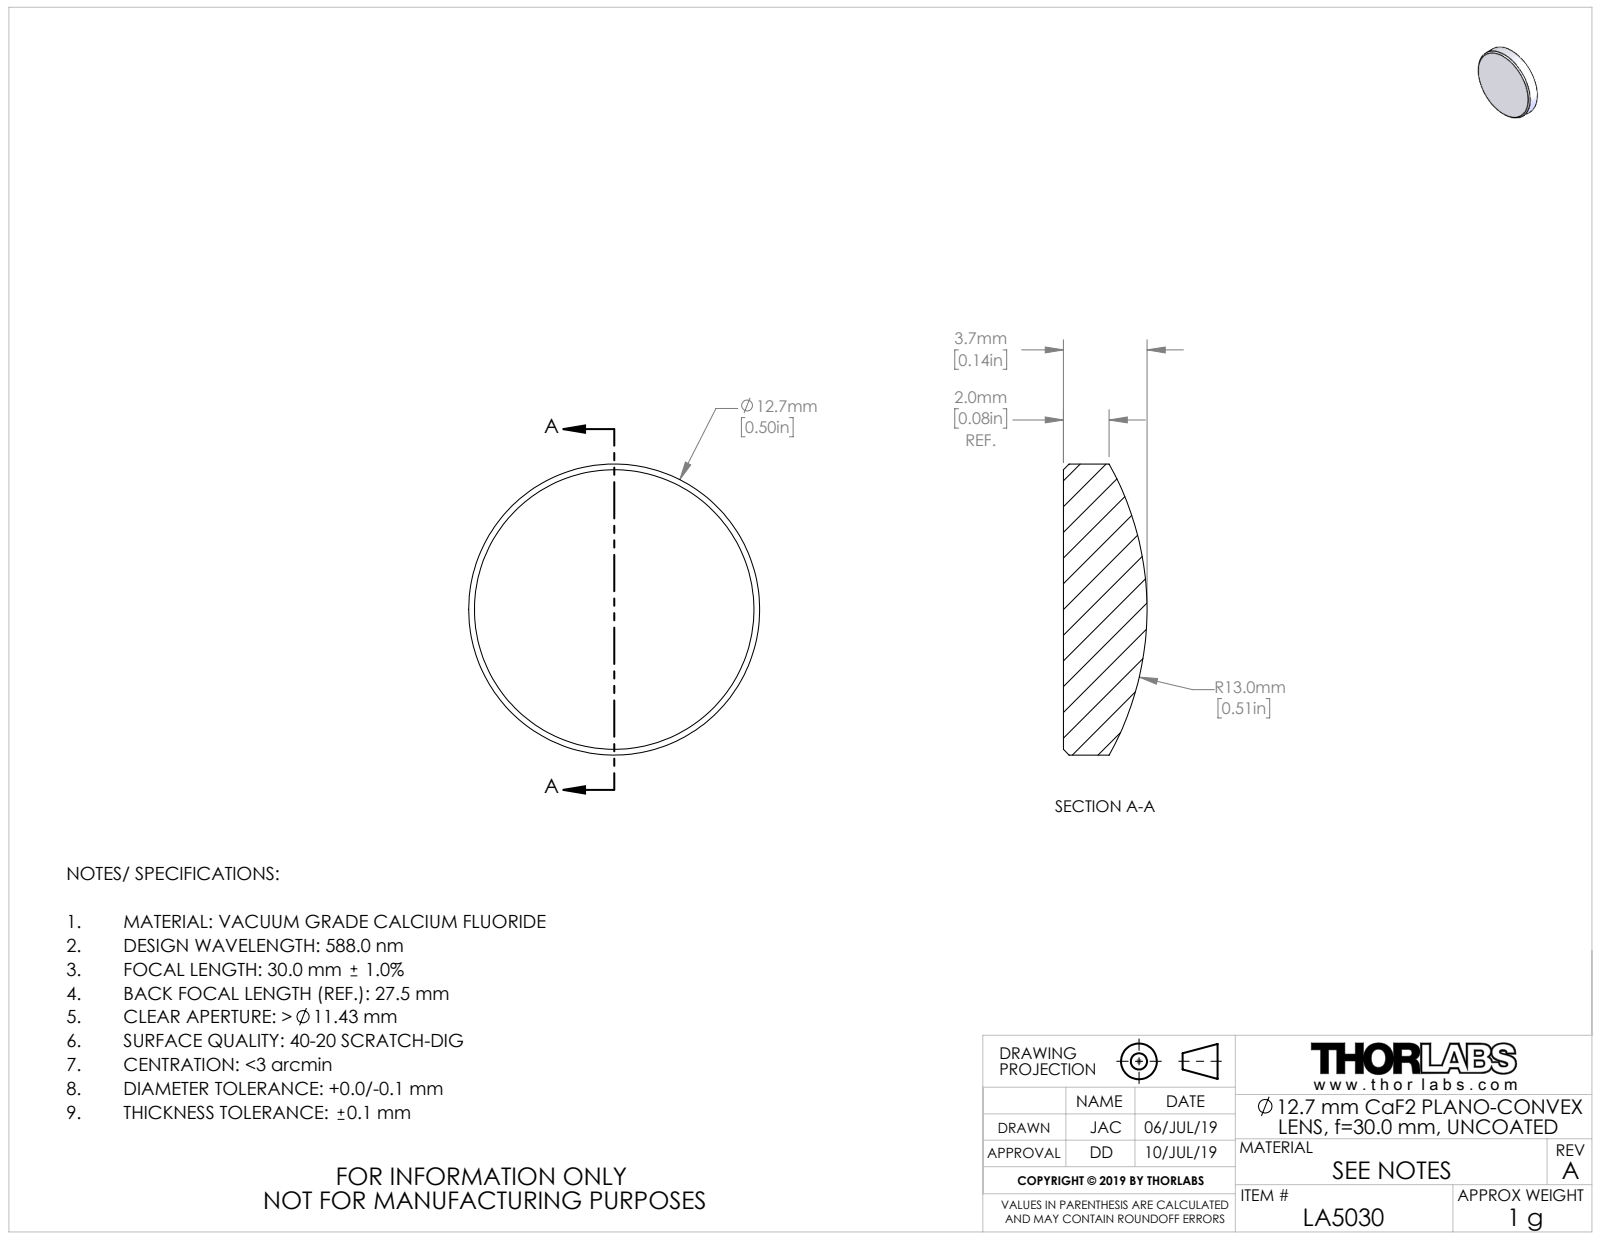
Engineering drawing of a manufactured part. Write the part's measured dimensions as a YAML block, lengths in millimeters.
part_name: "TTN188112-E0W"
step_written_by: "SolidWorks 2018 (CONFIG_CONTROL_DESIGN)"
units: millimeters
bodies: {solids: 1, faces: 7, planar: 1, cylindrical: 2, other: 4}
overall_size: [12.7, 12.7, 3.65]
volume: 359
surface_area: 336
round_bosses_or_shafts:
  - {diameter: 12.7, count: 1}
